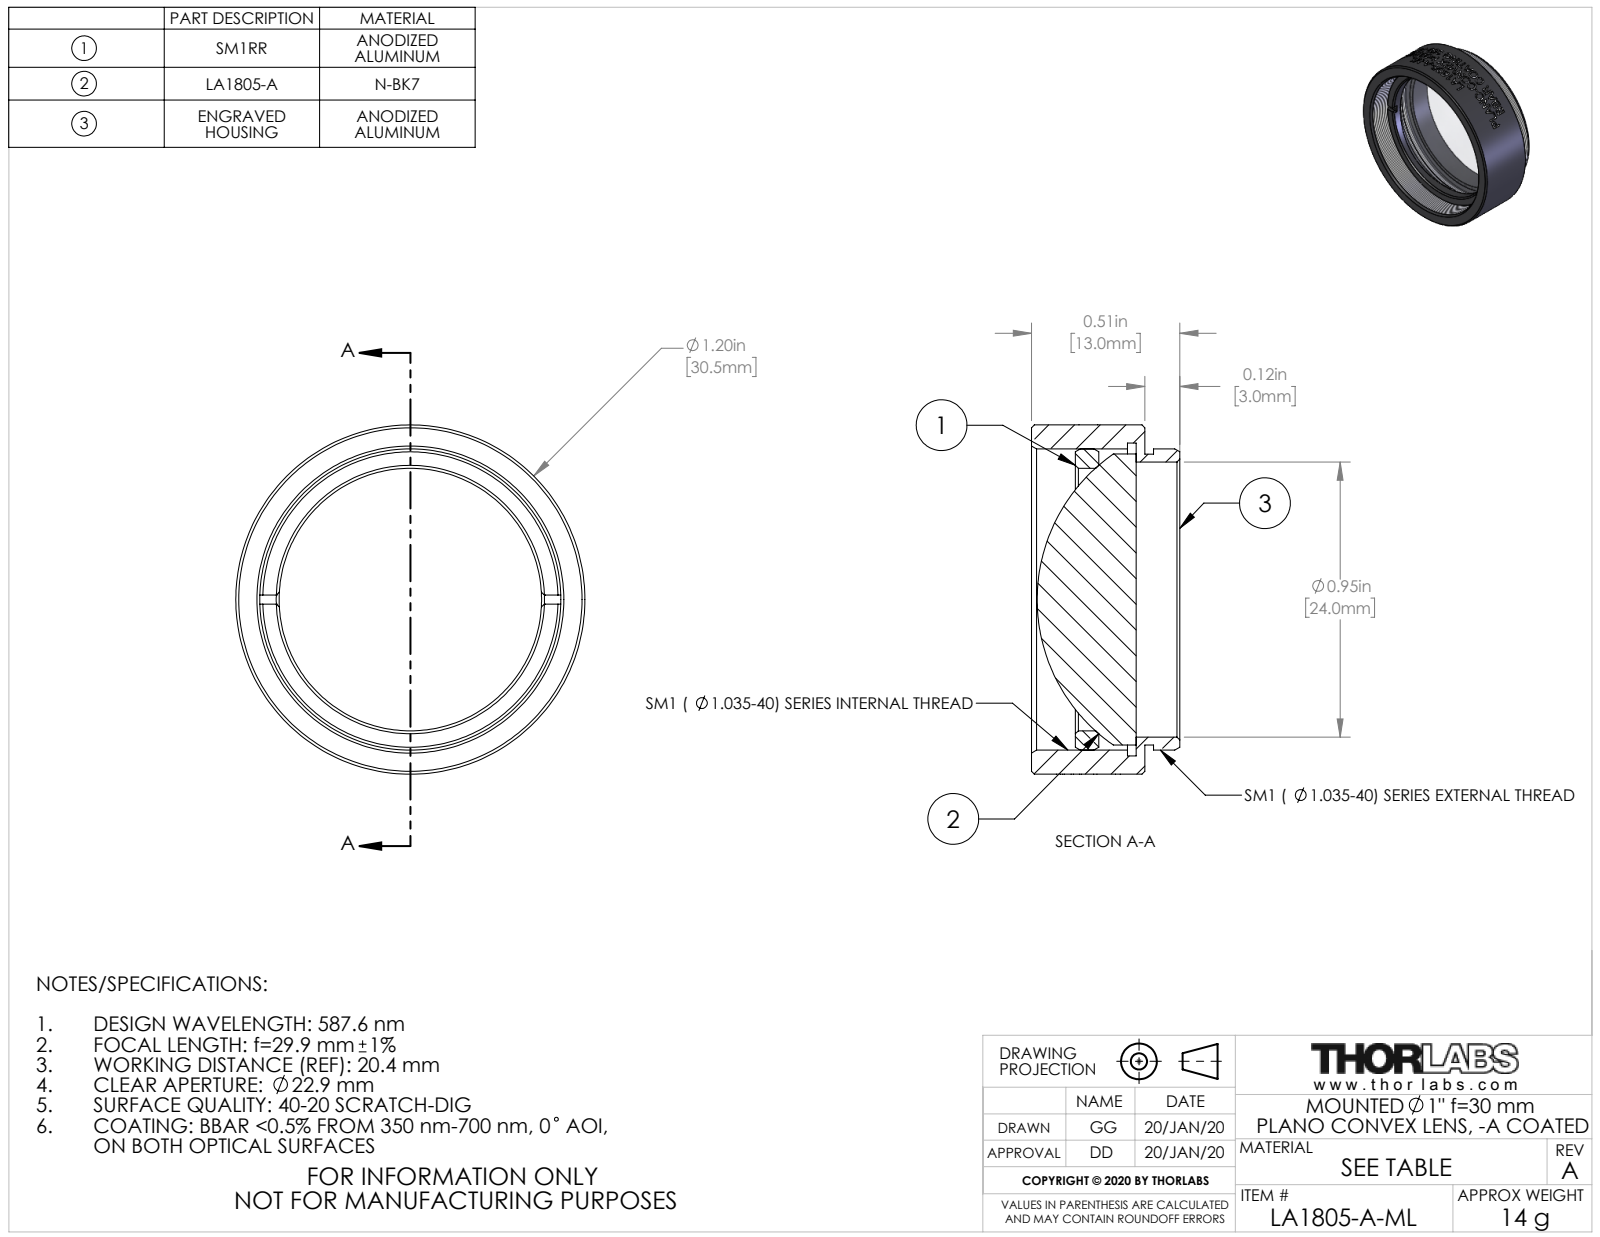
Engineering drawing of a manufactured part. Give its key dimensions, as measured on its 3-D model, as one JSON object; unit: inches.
{"part_name": "TTN203733-E0W", "step_written_by": "SolidWorks 2018 (CONFIG_CONTROL_DESIGN)", "units": "inches", "bodies": {"solids": 3, "faces": 155, "planar": 20, "cylindrical": 111, "other": 24}, "overall_size": [1.2, 1.2, 0.51], "volume_in3": 0.318, "surface_area_in2": 7.319, "round_holes": [[0.902, 1], [0.945, 1], [1.035, 1], [1.075, 1]], "round_bosses_or_shafts": [[1.2, 1], [1.035, 1], [1, 1], [0.999, 1]], "face_to_face_distances": [0.03, 0.39, 0.36, 0.159, 0.129, 0.231, 0.239, 0.209, 0.08, 0.152]}
